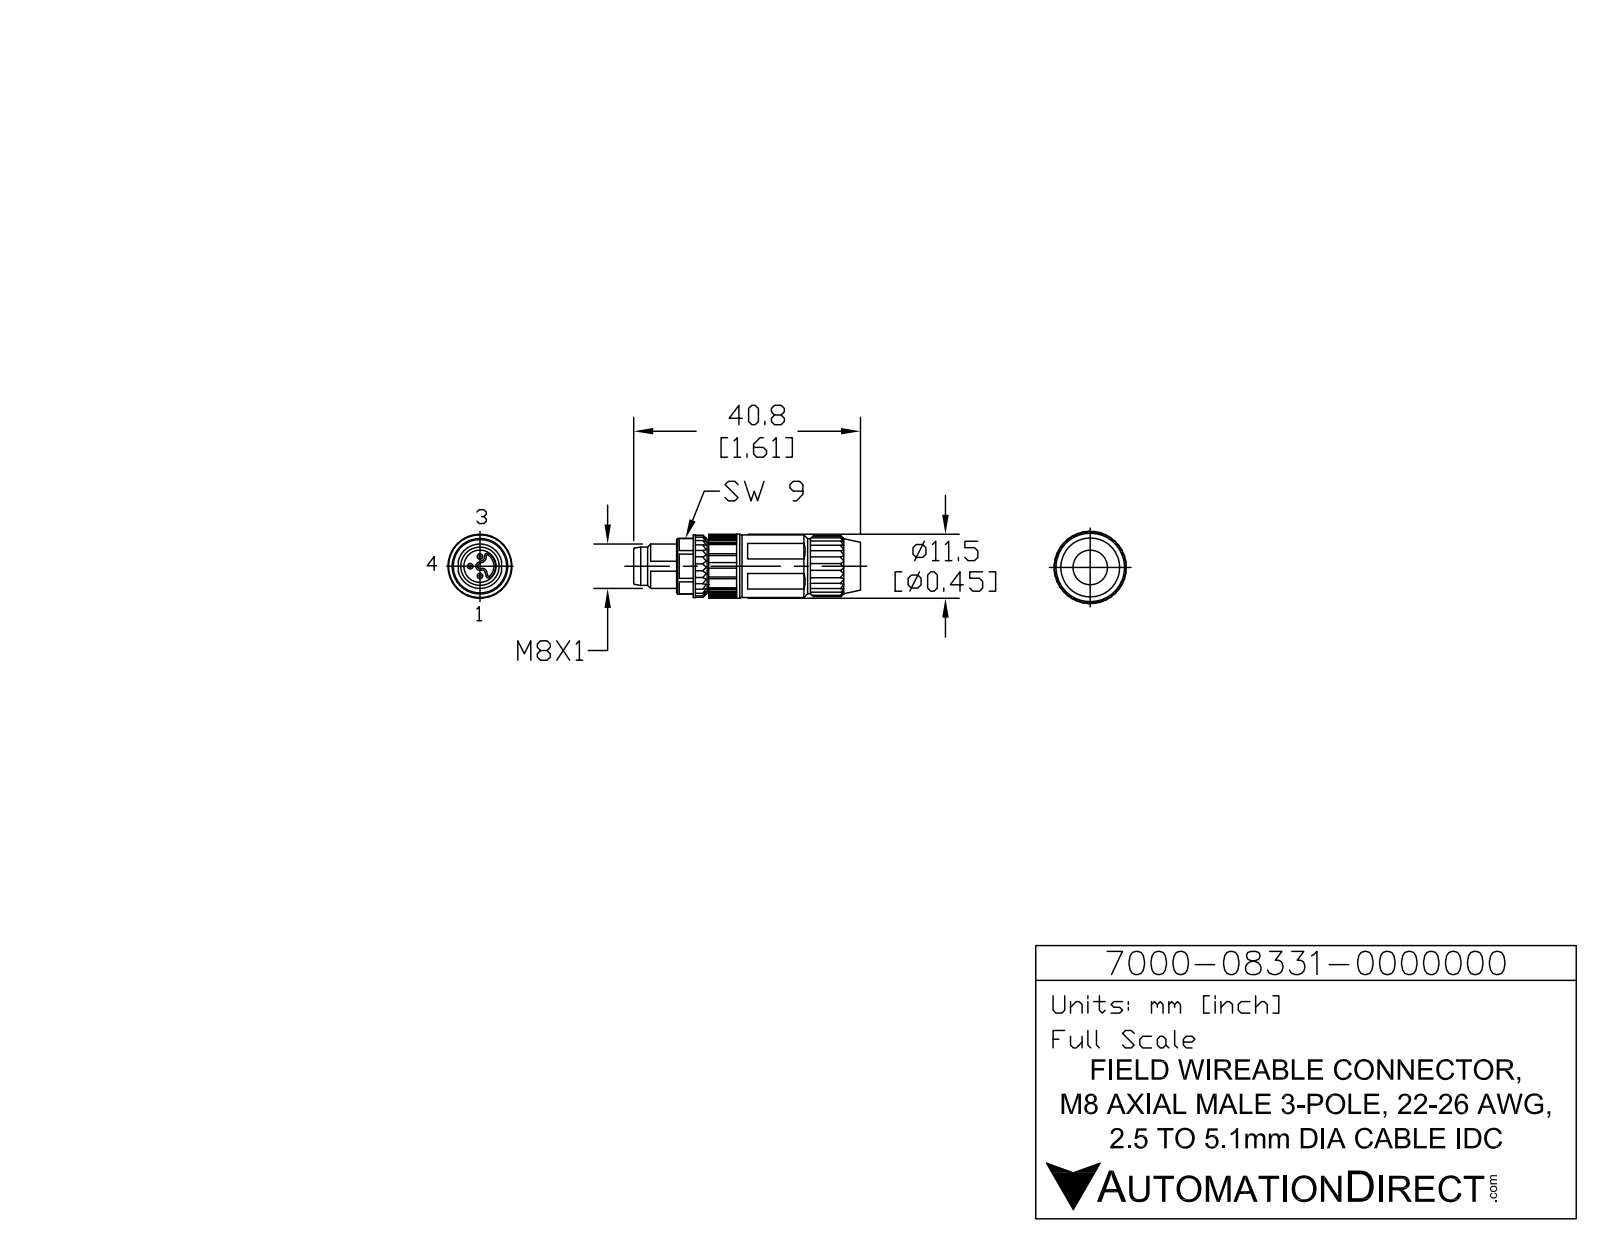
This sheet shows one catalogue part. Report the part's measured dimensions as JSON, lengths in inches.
{"part_name": "7000-08331-0000000", "step_written_by": "SolidWorks 2015 (AUTOMOTIVE_DESIGN)", "units": "inches", "bodies": {"solids": 1, "faces": 344, "planar": 238, "cylindrical": 58, "other": 48}, "overall_size": [1.606, 0.453, 0.453], "volume_in3": 0.16, "surface_area_in2": 3.884, "round_holes": [[0.22, 1], [0.225, 1]], "round_bosses_or_shafts": [[0.035, 3], [0.453, 1], [0.404, 1], [0.403, 1], [0.309, 1], [0.265, 1]], "face_to_face_distances": [0.127, 1.169, 1.296, 0.35, 0.787, 0.382, 0.509, 1.201, 0.413, 0.031]}
